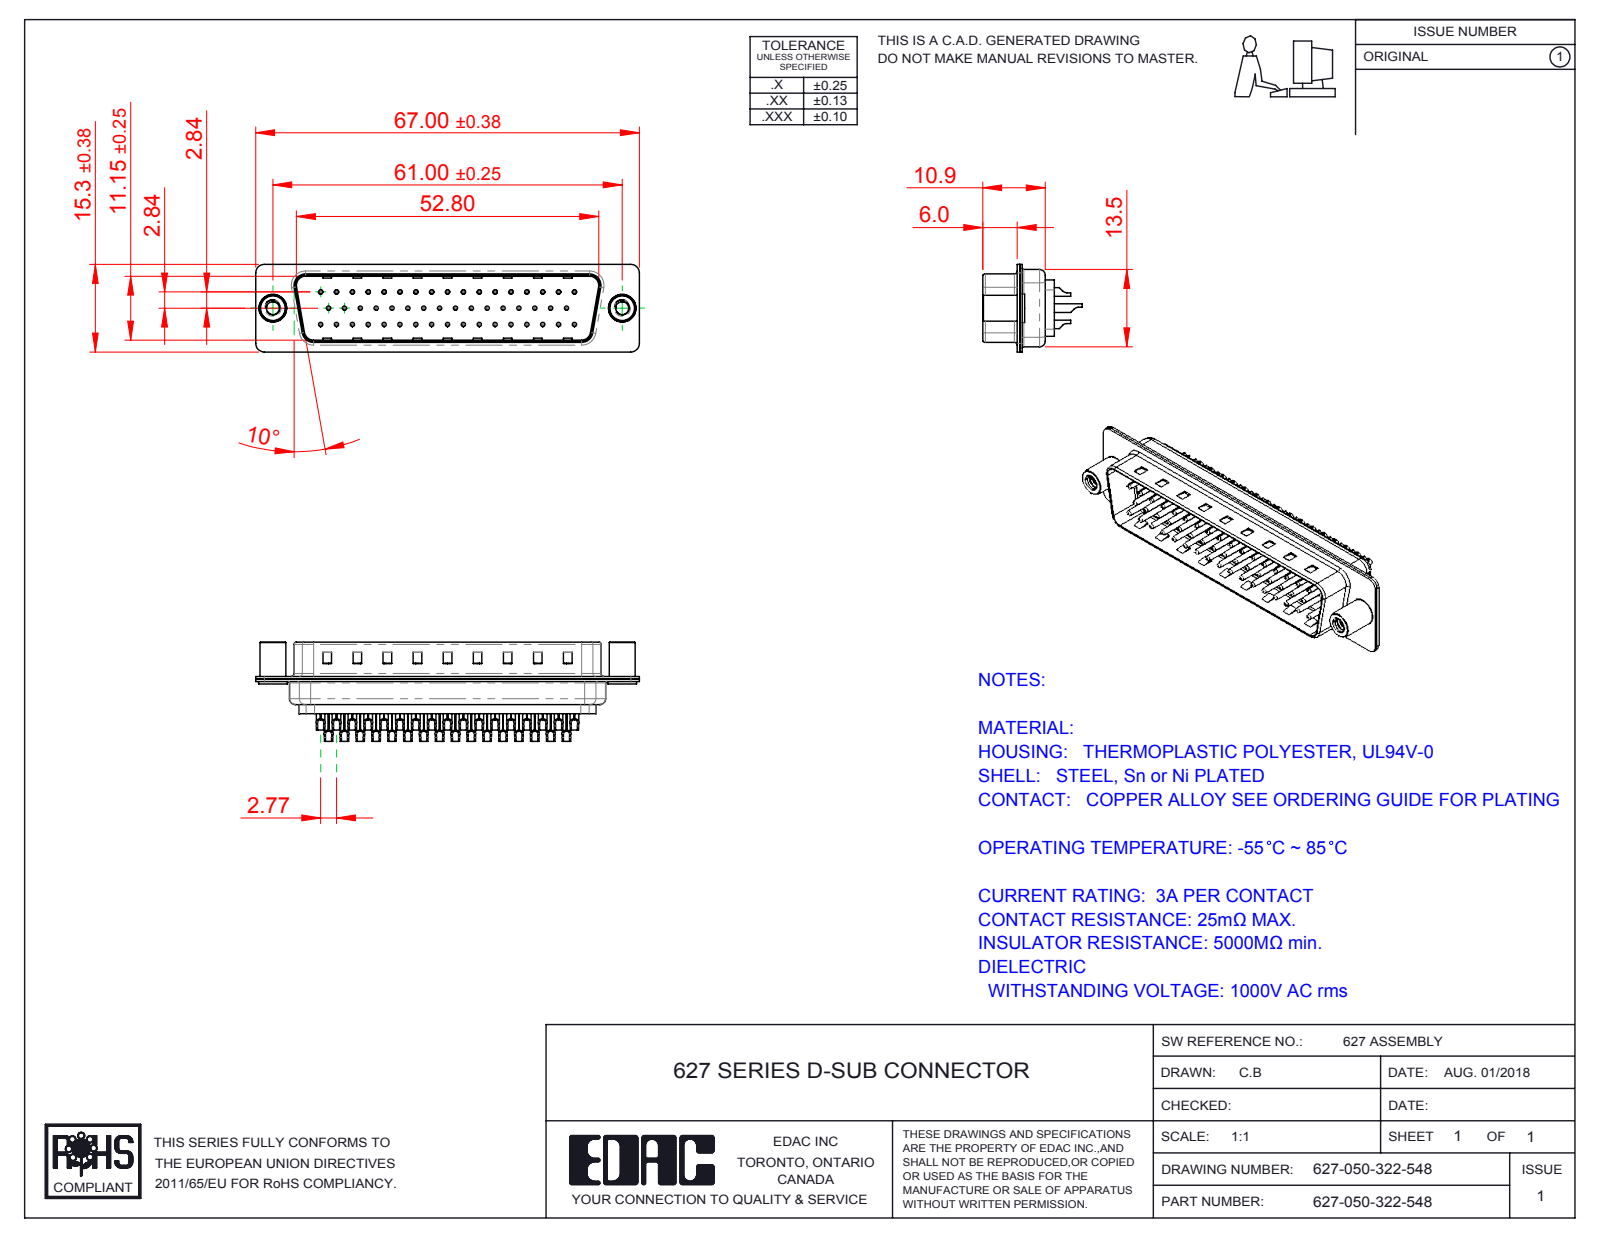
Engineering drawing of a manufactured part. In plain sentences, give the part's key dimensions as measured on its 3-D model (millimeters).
The part is named "627 Contact Row 2_22M; 627 Shell Front_50 Contacts; 627-050-322-548; 627 Housing_50 LP (+4 more)". Its 3-D file was written by "SolidWorks 2016 (CONFIG_CONTROL_DESIGN)". It is 55 solids with 3646 faces: 905 planar, 1619 cylindrical and 1122 other. Overall it measures 67 by 17.35 by 15.3 millimeters. Its volume is 4 531 cubic millimeters and its surface area 13 158 square millimeters. Round holes: 50 of diameter 0.35, 50 of diameter 1.1, 50 of diameter 1.6, 2 of diameter 2.26, 2 of diameter 4, 2 of diameter 4.8. Round bosses or shafts: 50 of diameter 2, 50 of diameter 1.5, 50 of diameter 0.75, 2 of diameter 5, 2 of diameter 4.9, 2 of diameter 4.5. Partial cylindrical surfaces (rounded edges, fillets, slot ends): 16 of radius 1.5, 12 of radius 2, 8 of radius 0.5, 8 of radius 1.6, 7 of radius 1, 4 of radius 0.25, 4 of radius 0.6, 4 of radius 0.65. The main face-to-face distances are 0.4, 0.45, 11.55, 0.9, 6.05, 6.5, 0.78, 12.33, 1.95, 0.77. The hole center spacings are 3.16, 2.77, 5.54, 8.31, 11.08, 13.85, 16.62, 5.03.
